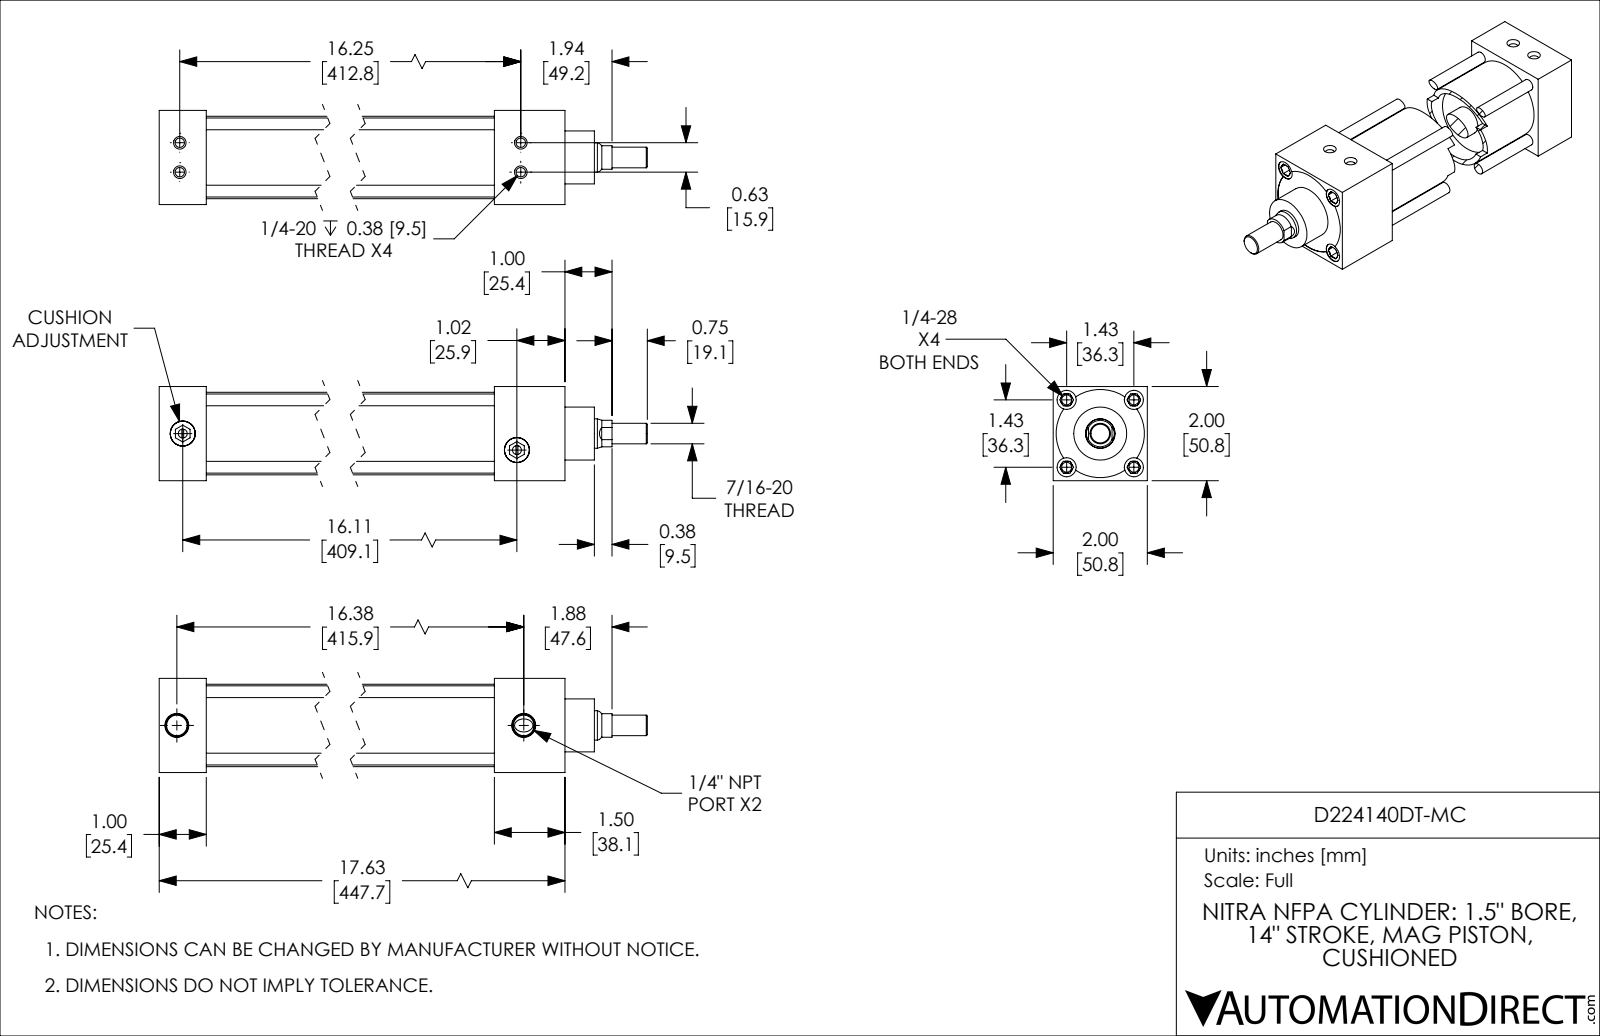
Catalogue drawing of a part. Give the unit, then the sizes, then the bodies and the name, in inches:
Units: inches
Overall size (bounding box): 19.375 × 2 × 2
Round holes (diameter × count): ⌀0.201 ×4, ⌀0.213 ×4, ⌀0.406 ×4, ⌀0.19 ×2, ⌀0.438 ×2, ⌀0.531 ×2, ⌀0.626 ×1, ⌀1.501 ×1
Round bosses / shafts (diameter × count): ⌀0.25 ×4, ⌀0.532 ×2, ⌀1.751 ×1, ⌀1.499 ×1, ⌀1.125 ×1, ⌀0.624 ×1, ⌀0.437 ×1
Partial cylindrical surfaces — rounded edges, fillets, slot ends (radius × count): R0.281 ×1, R0.937 ×1
Main face-to-face distances: 2, 1, 16.125, 15.125, 17.62, 16.62, 1.495, 1.125, 2.125, 14
Hole centre spacings: 0.319, 1.011, 1.43, 0.625, 2.022, 16.25, 16.262, 16.315
Volume: 29.14 in³ · Surface area: 293.3 in²
Bodies: 4 solids, 251 faces (90 planar, 81 cylindrical, 80 other)
Part name (STEP PRODUCT): D224140DT-MC_BODY; D224140DT-MC; D224140DT-MC_CUSHION; D224140DT-MC_PISTON_KK1
STEP written by: SolidWorks 2019 (CONFIG_CONTROL_DESIGN)
